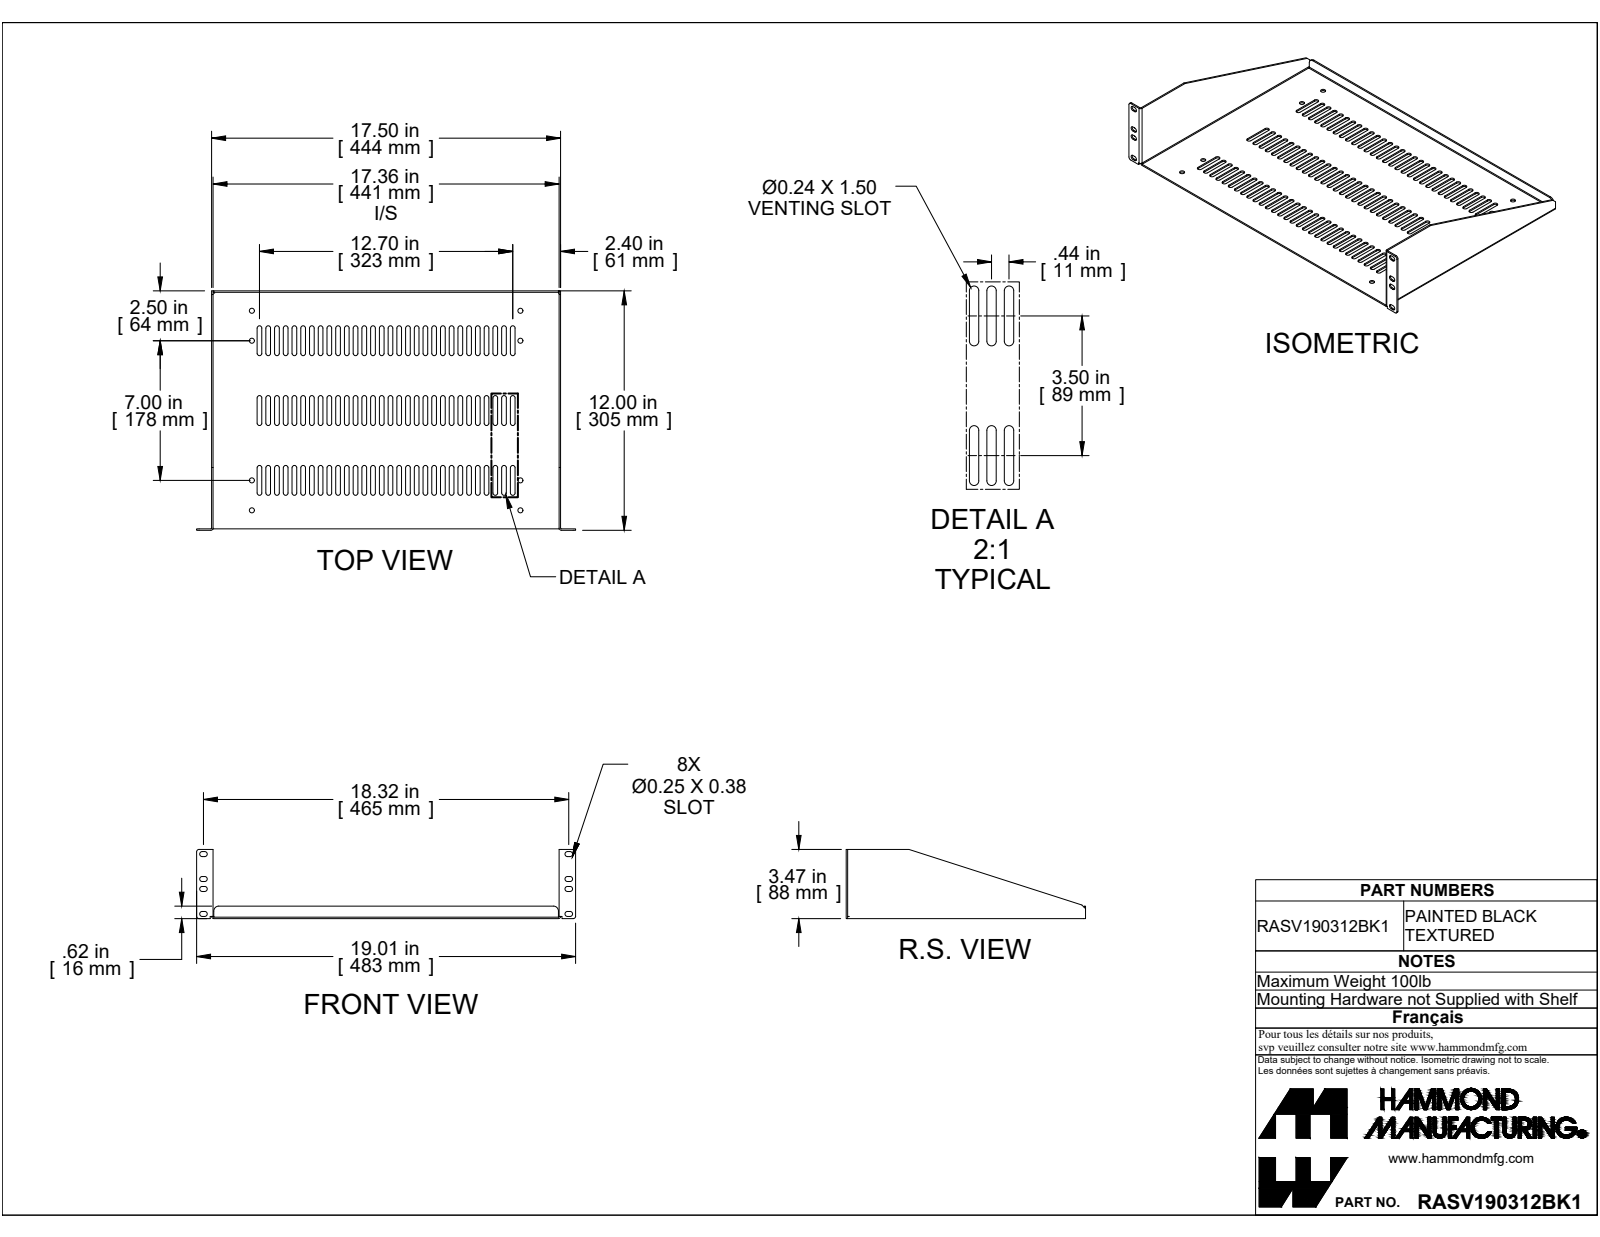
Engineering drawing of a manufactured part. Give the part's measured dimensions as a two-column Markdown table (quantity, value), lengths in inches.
| quantity | value |
| --- | --- |
| part name | RASV190312BK1 |
| STEP written by | SolidWorks 2019 (CONFIG_CONTROL_DESIGN) |
| units | inches |
| bodies | 1 solid, 456 faces (236 planar, 220 cylindrical, 0 other) |
| overall size | 19.006 × 12 × 3.468 |
| volume | 17.76 in³ |
| surface area | 520.6 in² |
| round holes (diameter × count) | 0.25 × 8 |
| partial cylindrical surfaces (radius × count) | 0.118 × 174, 0.125 × 20, 0.117 × 6, 0.036 × 5, 0.108 × 5, 0.25 × 2 |
| main face-to-face distances | 0.072, 17.428, 17.356, 17.5, 11.856, 11.928, 0.072, 11.928, 12, 0.876 |
| hole center spacings | 1.5, 8.5, 13.468, 13.551, 15.926, 7, 10, 15.178 |
